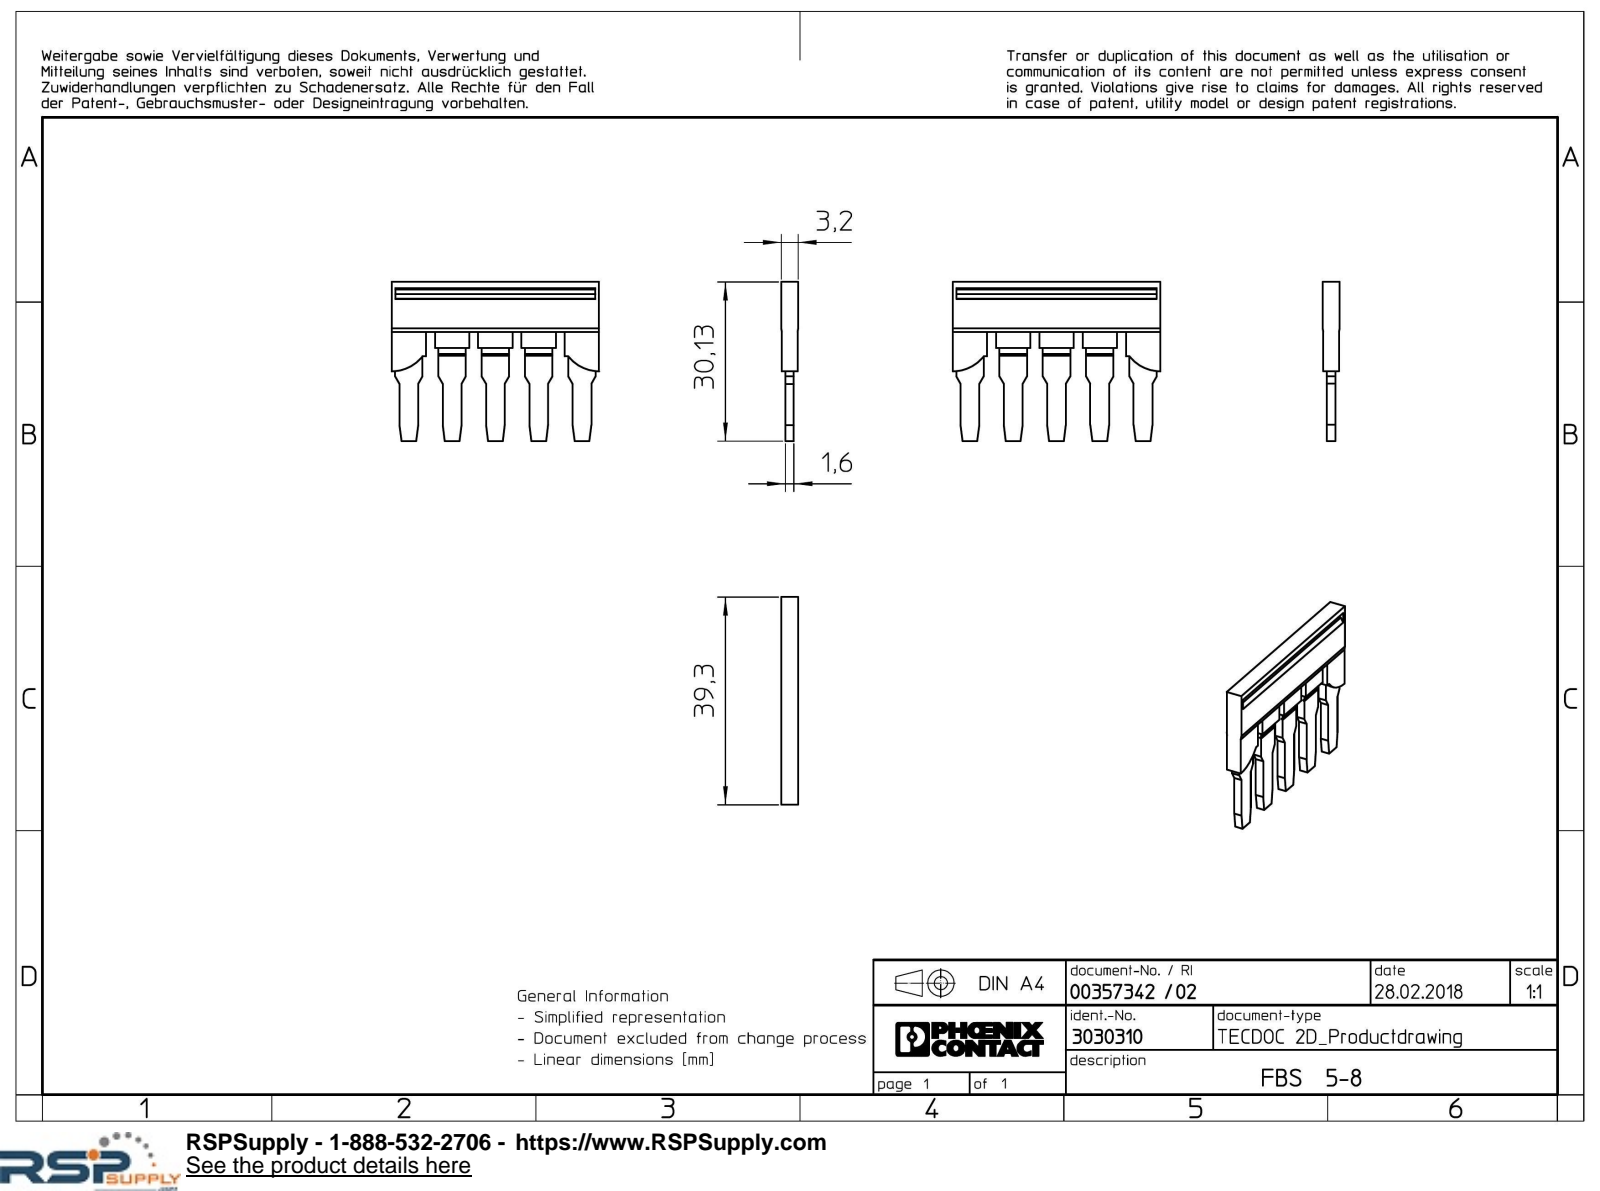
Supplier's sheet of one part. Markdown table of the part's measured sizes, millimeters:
| quantity | value |
| --- | --- |
| part name | FBS_5_8-select |
| STEP written by | Creo Elements/Direct Modeling 20.1A 29-Sep-2018 (C) Parametric Technology GmbH (AUTOMOTIVE_DESIGN) |
| units | millimeters |
| bodies | 1 solid, 121 faces (119 planar, 2 cylindrical, 0 other) |
| overall size | 39.3 × 30.12 × 3.2 |
| volume | 2 035 mm³ |
| surface area | 2 468 mm² |
| partial cylindrical surfaces (radius × count) | 7.45 × 2 |
| main face-to-face distances | 0.8, 2.4, 1.6, 3.1, 0.7, 2.3, 3.2, 8.2, 3, 16.4 |
